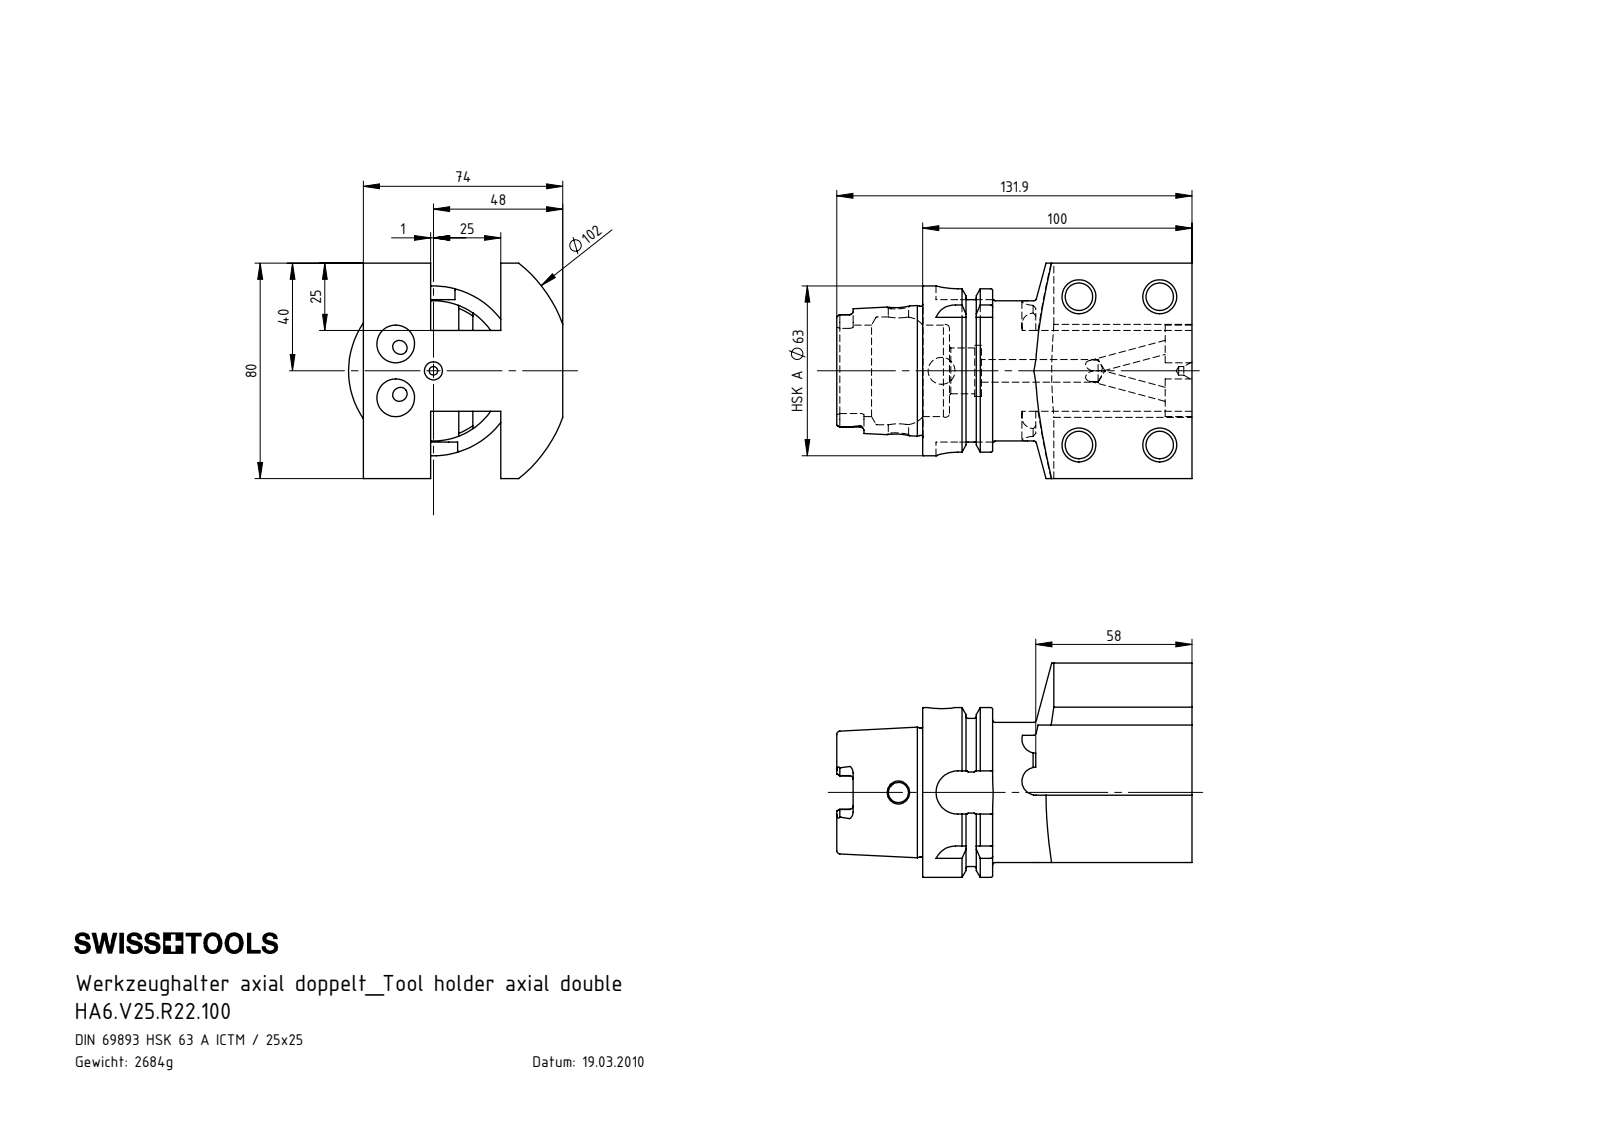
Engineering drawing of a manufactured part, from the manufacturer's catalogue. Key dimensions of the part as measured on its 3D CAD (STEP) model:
Part name (STEP PRODUCT): HA6-V25.R22.100; KU1-U14.001.012_2; KU1-U14.001.012; KU1-U14.001.012_1 (+2 more)
STEP written by: SolidWorks 2017 (CONFIG_CONTROL_DESIGN)
Units: millimetres
Bodies: 9 solids, 232 faces (101 planar, 56 cylindrical, 75 other)
Overall size (bounding box): 134.71 × 80 × 79.5
Volume: 354 063 mm³ · Surface area: 64 216 mm²
Round holes (diameter × count): ⌀5 ×4, ⌀10.2 ×4, ⌀10 ×3, ⌀14 ×2, ⌀3.15 ×1, ⌀7.5 ×1, ⌀8.4 ×1, ⌀17 ×1, ⌀19 ×1, ⌀34 ×1, ⌀40 ×1
Round bosses / shafts (diameter × count): ⌀12 ×4, ⌀63 ×1, ⌀54.95 ×1, ⌀52 ×1, ⌀47.94 ×1
Partial cylindrical surfaces — rounded edges, fillets, slot ends (radius × count): R1.4 ×6, R2.88 ×4, R8 ×4, R5.2 ×2, R51 ×1
Main face-to-face distances: 25, 55, 51, 26, 23, 49, 74, 80, 30, 100
Hole centre spacings: 17.2, 30, 55, 57.94, 62.65, 85.54, 20
